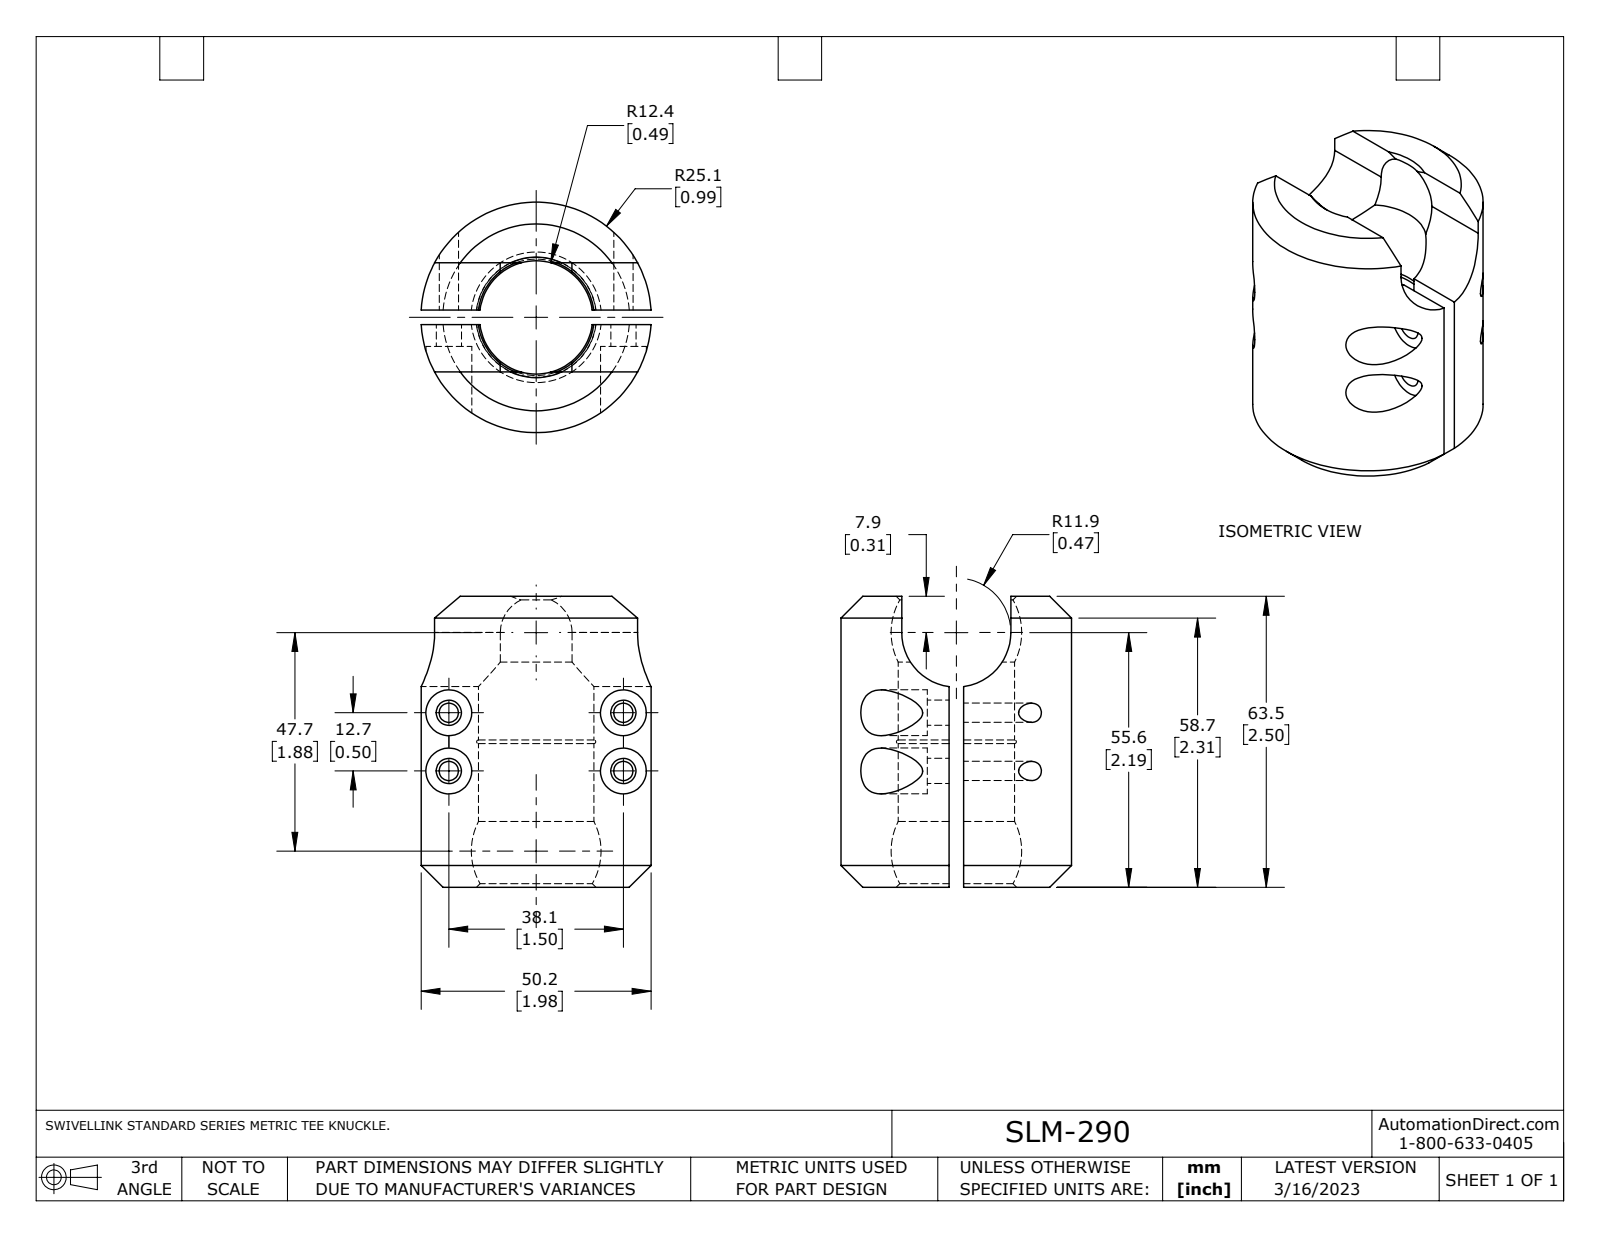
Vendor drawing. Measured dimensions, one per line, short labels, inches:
name: SLM-290
written by: SolidWorks 2021 (AUTOMOTIVE_DESIGN)
unit: in
bodies: 2 solids, 52 faces (16 planar, 22 cylindrical, 14 other)
size: 2.5 × 1.98 × 1.976
volume: 4.332 in³; area: 30.38 in²
holes: 4× ⌀0.165, 4× ⌀0.217, 4× ⌀0.394, 1× ⌀1
bosses: 1× ⌀1.98
rounds: 1× R0.469
face distances: 0.125, 0.406, 0.531, 2.5, 0.938, 0.719, 0.313, 0.187, 0.219
hole spacings: 0.5, 1.5, 1.581
